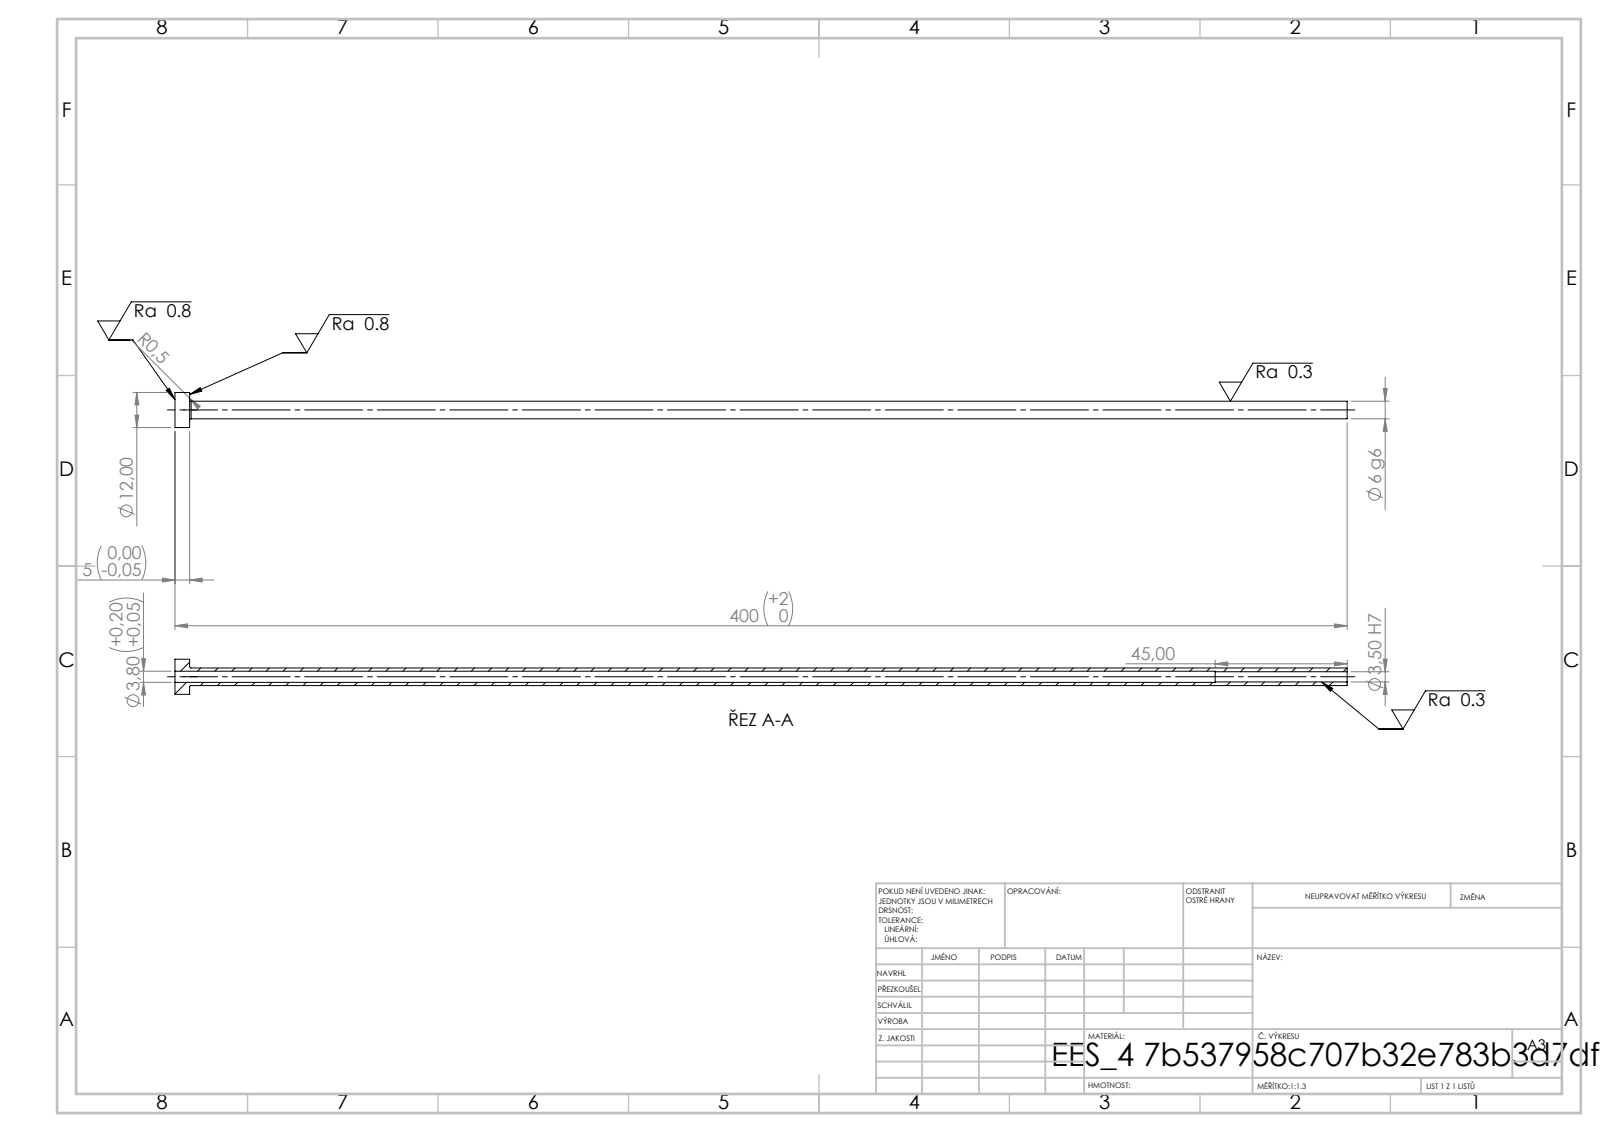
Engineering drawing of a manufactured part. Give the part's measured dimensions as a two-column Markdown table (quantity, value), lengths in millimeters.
| quantity | value |
| --- | --- |
| STEP written by | SolidWorks 2019 (CONFIG_CONTROL_DESIGN) |
| units | millimeters |
| bodies | 1 solid, 14 faces (4 planar, 8 cylindrical, 2 other) |
| overall size | 400 × 12 × 12 |
| volume | 7 276 mm³ |
| surface area | 12 570 mm² |
| round holes (diameter × count) | 3.5 × 1, 3.8 × 1 |
| round bosses / shafts (diameter × count) | 12 × 1, 6 × 1 |
| main face-to-face distances | 5, 400, 395, 355, 350, 45 |
